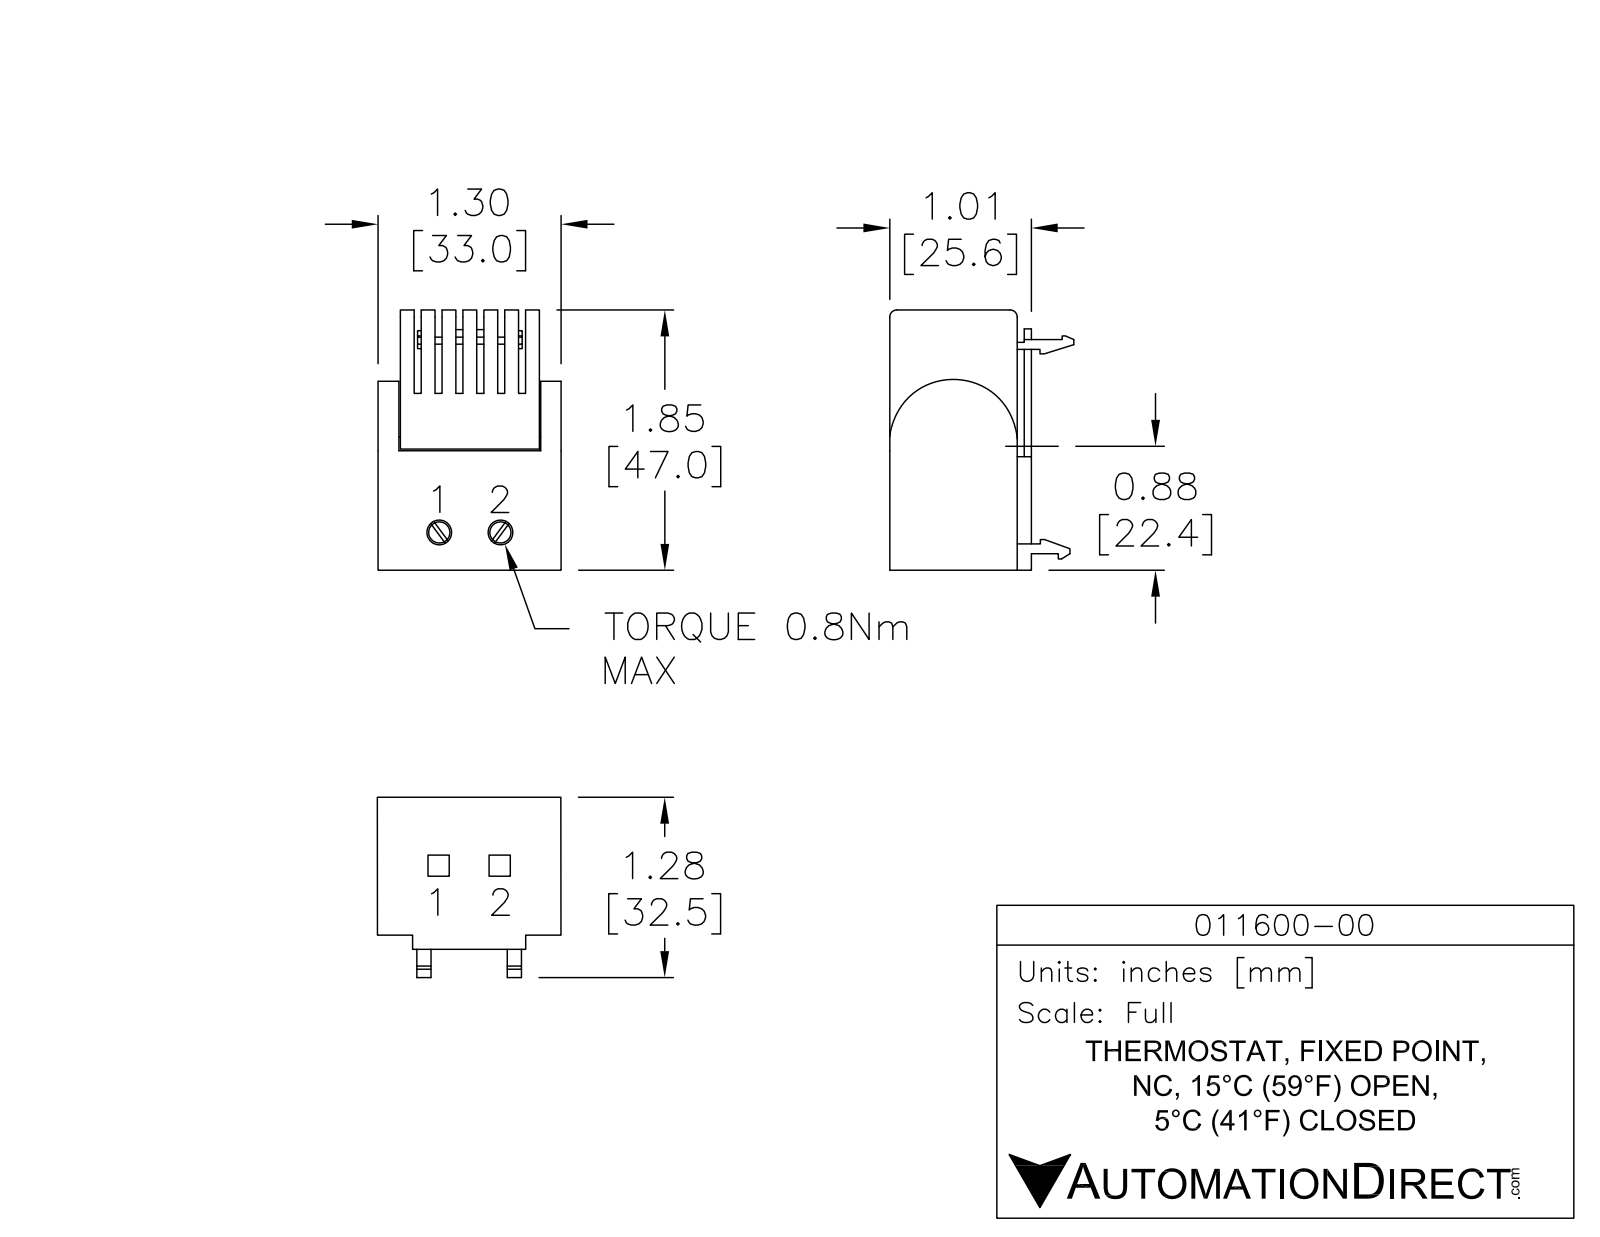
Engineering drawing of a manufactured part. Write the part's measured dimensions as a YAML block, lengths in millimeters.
part_name: "011600-00"
step_written_by: "SolidWorks 2013 (AUTOMOTIVE_DESIGN)"
units: millimeters
bodies: {solids: 1, faces: 374, planar: 188, cylindrical: 123, other: 63}
overall_size: [46.3, 33.1, 32.6]
volume: 32590
surface_area: 10040
partial_cylinders:
  - {radius: 0.6, count: 16}
  - {radius: 0.6, count: 10}
  - {radius: 0.8, count: 8}
  - {radius: 0.4, count: 7}
  - {radius: 1.5, count: 7}
  - {radius: 1, count: 4}
  - {radius: 0.7, count: 3}
  - {radius: 0.7, count: 2}
face_to_face_distances: [33.1, 2.4, 23.1, 23.1, 4.5, 28.6, 3.6, 7.1, 0.7, 46.3]
